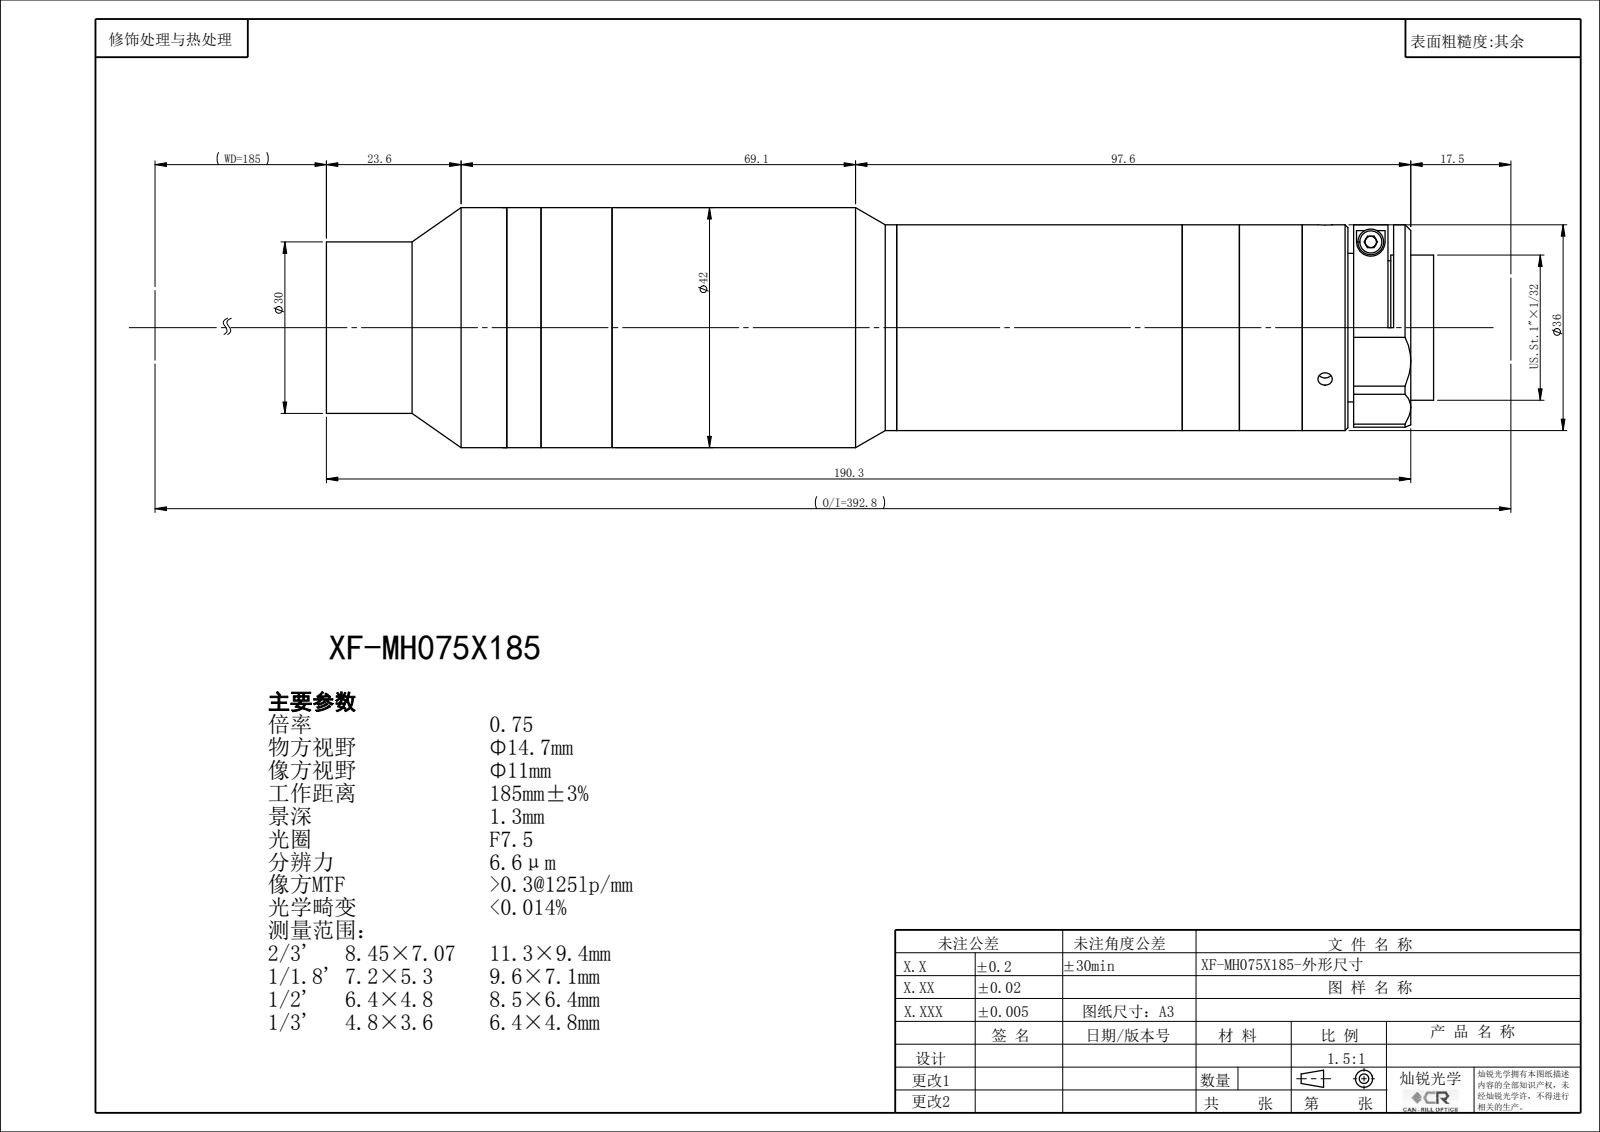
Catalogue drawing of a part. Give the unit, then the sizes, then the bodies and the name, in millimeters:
Units: millimetres
Overall size (bounding box): 194.28 × 42 × 42
Round holes (diameter × count): ⌀2.5 ×3, ⌀22.4 ×1, ⌀24 ×1, ⌀26.4 ×1
Round bosses / shafts (diameter × count): ⌀42 ×1, ⌀36 ×1, ⌀34 ×1, ⌀30 ×1, ⌀25.4 ×1
Main face-to-face distances: 1.5, 28.95, 30.45, 50, 60, 88.95, 90.45, 10, 38.95, 40.45
Bodies: 0 solids, 137 faces (67 planar, 46 cylindrical, 24 other)
Part name (STEP PRODUCT): XF-MH075X185
STEP written by: SolidWorks 2022 (CONFIG_CONTROL_DESIGN)
